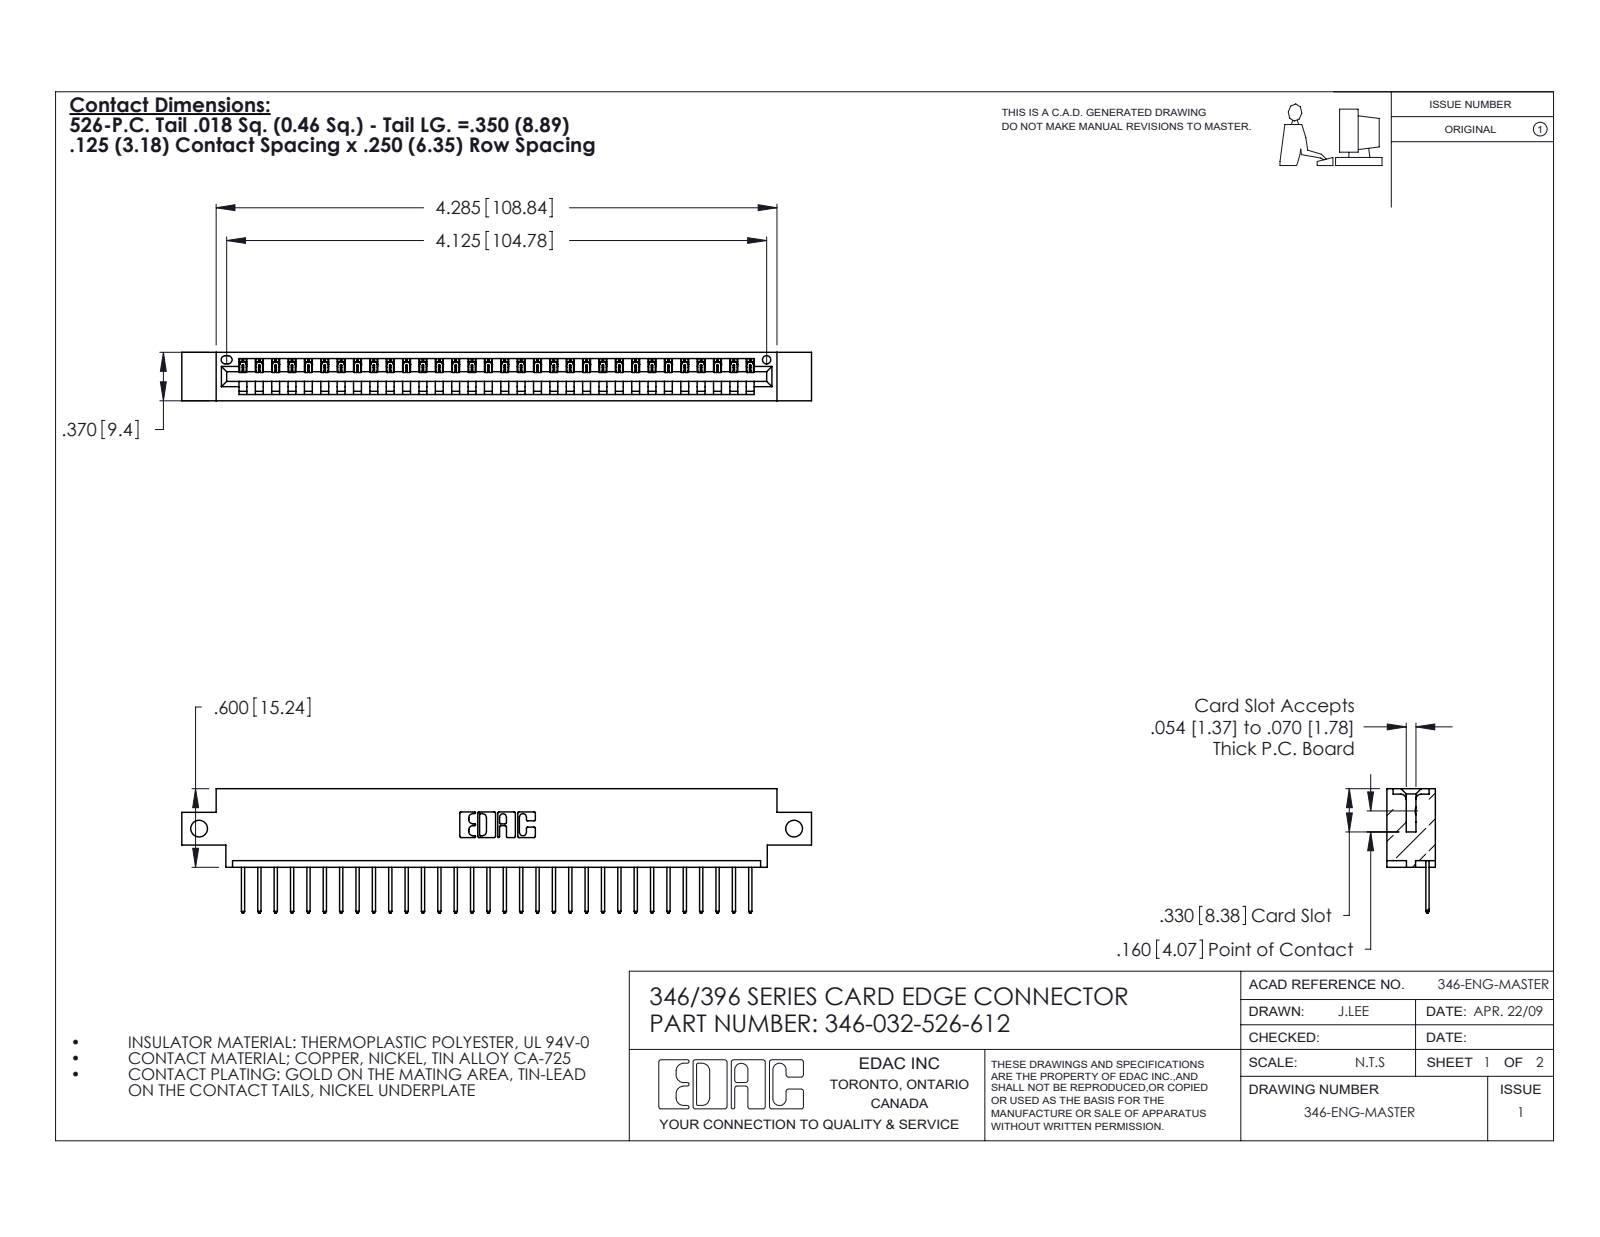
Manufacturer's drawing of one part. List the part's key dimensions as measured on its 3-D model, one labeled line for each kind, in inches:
Part name (STEP PRODUCT): 346 Part_0.170 Offset - Side Mount; 346-032-526-612; 345-292-001_345-293-126
STEP written by: SolidWorks 2020 (CONFIG_CONTROL_DESIGN)
Units: inches
Bodies: 33 solids, 1982 faces (1360 planar, 622 cylindrical, 0 other)
Overall size (bounding box): 4.81 × 0.95 × 0.37
Volume: 0.693 in³ · Surface area: 21.81 in²
Round holes (diameter × count): ⌀0.128 ×2, ⌀0.064 ×1
Partial cylindrical surfaces — rounded edges, fillets, slot ends (radius × count): R0.006 ×64, R0.01 ×64, R0.01 ×22, R0.007 ×6, R0.031 ×6, R0.026 ×3, R0.031 ×2, R0.04 ×2
Main face-to-face distances: 0.048, 0.322, 0.37, 0.25, 0.072, 0.298, 0.025, 0.148, 0.222, 0.1
Hole centre spacings: 4.545
